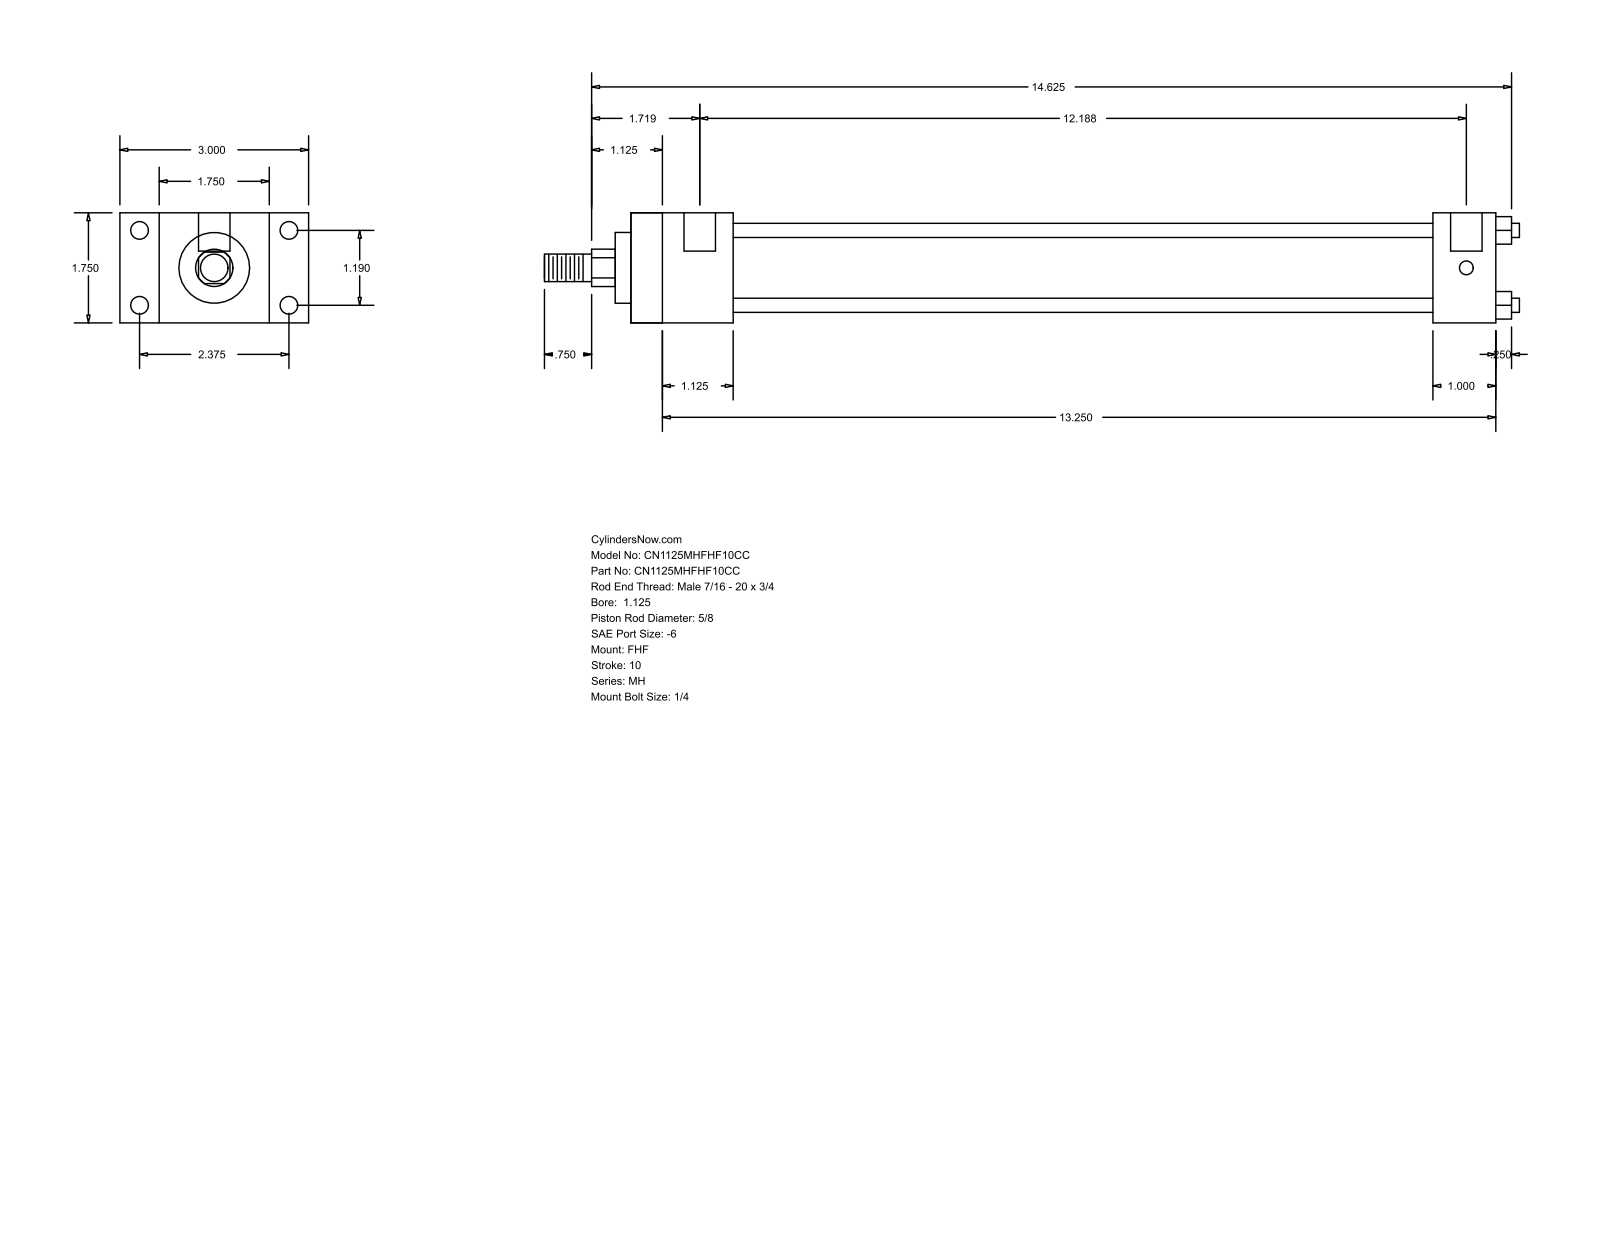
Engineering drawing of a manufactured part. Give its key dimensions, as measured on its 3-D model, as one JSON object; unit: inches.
{"part_name": "MH_FHF__0112_0.625", "step_written_by": "GSSL Pune (CONFIG_CONTROL_DESIGN)", "units": "inches", "bodies": {"solids": 0, "faces": 88, "planar": 60, "cylindrical": 28, "other": 0}, "overall_size": [15.5, 3, 1.75], "round_holes": [[0.219, 4], [0.281, 4], [0.5, 2]], "round_bosses_or_shafts": [[0.225, 4], [1.375, 1], [1.125, 1], [0.625, 1], [0.437, 1]], "partial_cylinders_radius": [[0.297, 1]], "face_to_face_distances": [1.75, 0.625, 2.375, 1.625, 3, 13.75, 12.125, 12.75, 11.125, 1], "hole_center_spacings": [1.19, 2.375, 2.656, 12.063, 0.125, 12.187]}
